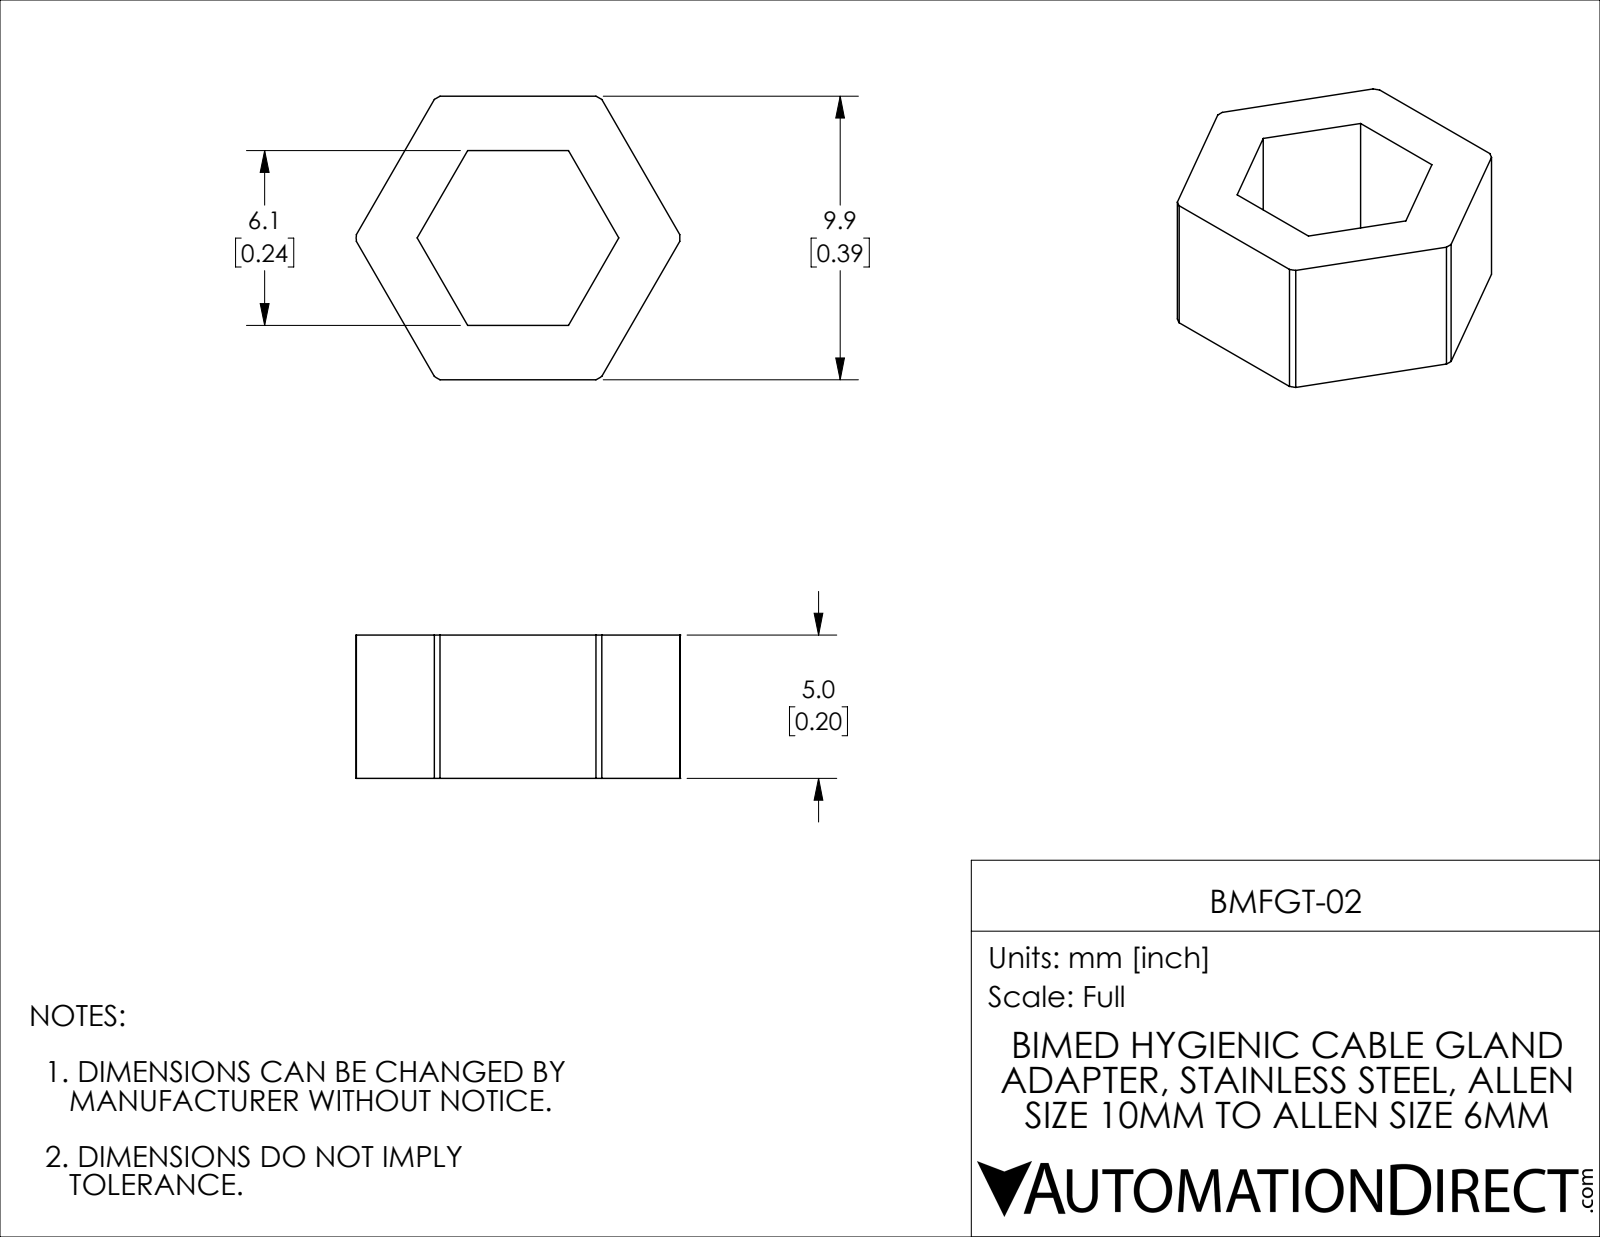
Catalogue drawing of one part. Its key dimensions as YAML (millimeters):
part_name: "BMFGT-02"
step_written_by: "SolidWorks 2021 (CONFIG_CONTROL_DESIGN)"
units: millimeters
bodies: {solids: 1, faces: 22, planar: 14, cylindrical: 8, other: 0}
overall_size: [11.3, 9.9, 5]
volume: 263
surface_area: 381
partial_cylinders:
  - {radius: 5.65, count: 1}
face_to_face_distances: [8, 1.9, 9.9, 6.1, 5]
